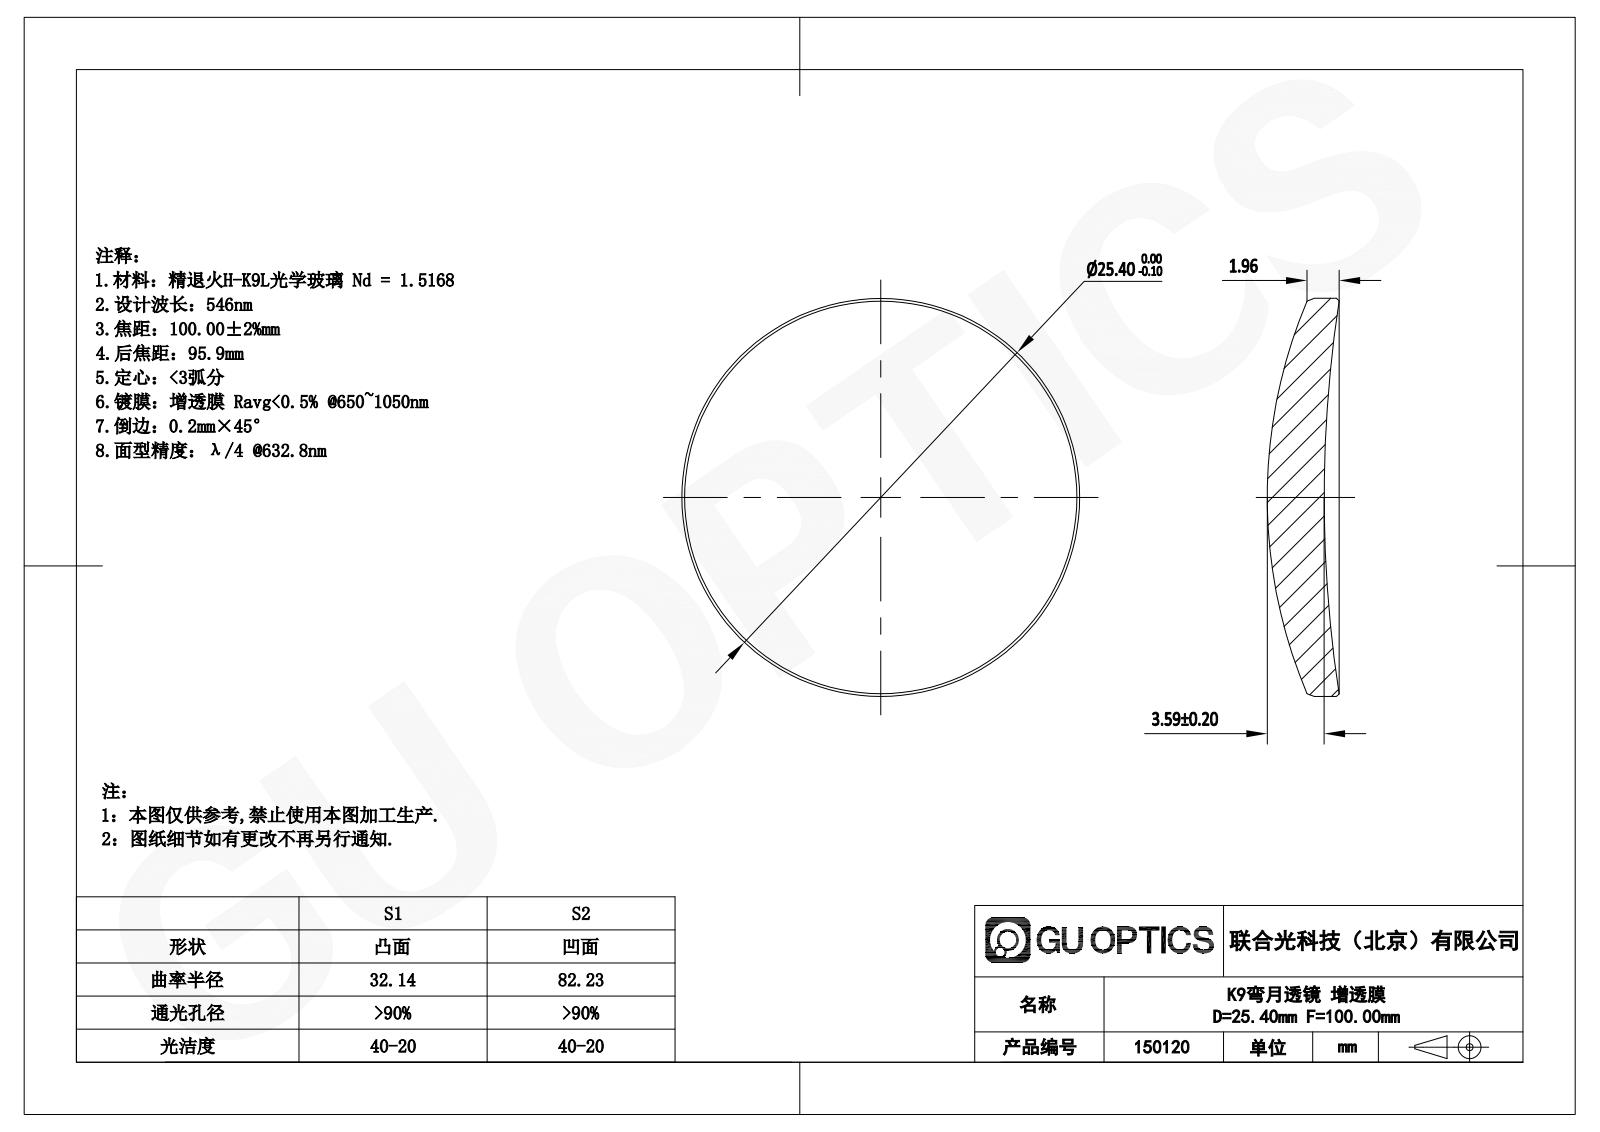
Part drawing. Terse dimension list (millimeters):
name: GLM1-025B-100-NIR
written by: SolidWorks 2022 (AUTOMOTIVE_DESIGN)
unit: mm
bodies: 1 solid, 10 faces (0 planar, 2 cylindrical, 8 other)
size: 25.4 × 25.4 × 4.59
volume: 1 431 mm³; area: 1 180 mm²
bosses: 1× ⌀25.4
